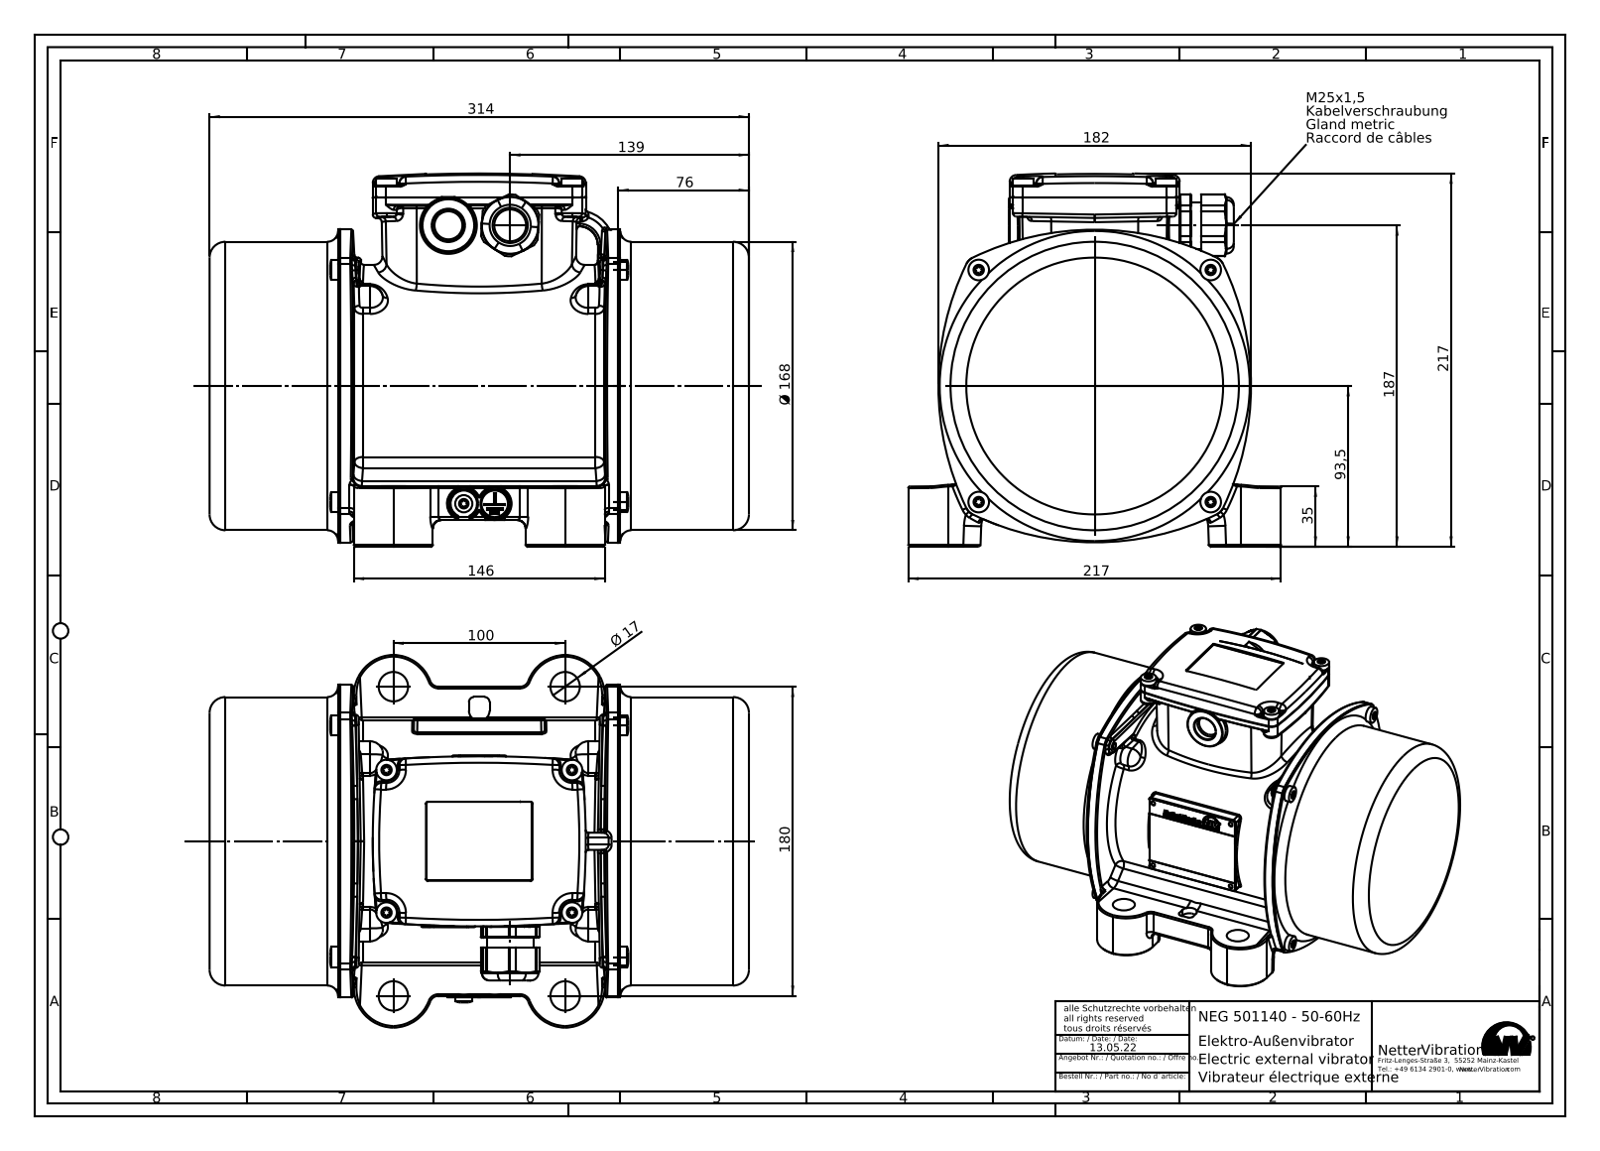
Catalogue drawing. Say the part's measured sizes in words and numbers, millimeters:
The part is named "NEG 501140-50-60Hz". Its 3-D file was written by "SolidWorks 2015 (AUTOMOTIVE_DESIGN)". It is 27 solids with 3140 faces: 954 planar, 731 cylindrical and 1455 other. Overall it measures 314 by 217.21 by 216.99 millimeters. Its volume is 1 450 000 cubic millimeters and its surface area 648 595 square millimeters. Round holes: 4 of diameter 3.4, 4 of diameter 5, 4 of diameter 6.5, 4 of diameter 6.8, 4 of diameter 9, 2 of diameter 16, 1 of diameter 8.8, 1 of diameter 11, 1 of diameter 18.5, 1 of diameter 23.6, 1 of diameter 125.3, 1 of diameter 130. Round bosses or shafts: 8 of diameter 12, 8 of diameter 6, 2 of diameter 10, 2 of diameter 5, 1 of diameter 167.9, 1 of diameter 165, 1 of diameter 164.8, 1 of diameter 141. Partial cylindrical surfaces (rounded edges, fillets, slot ends): 26 of radius 0.5, 25 of radius 2, 24 of radius 10, 22 of radius 1, 19 of radius 5, 18 of radius 0.3, 12 of radius 1.5, 10 of radius 1.75. The main face-to-face distances are 1.2, 312.8, 74.8, 238, 311.6, 314, 76, 236.8, 5, 167. The hole center spacings are 119, 24.51, 70.99, 95.5, 100.4, 135.06, 166.5, 47.59.
